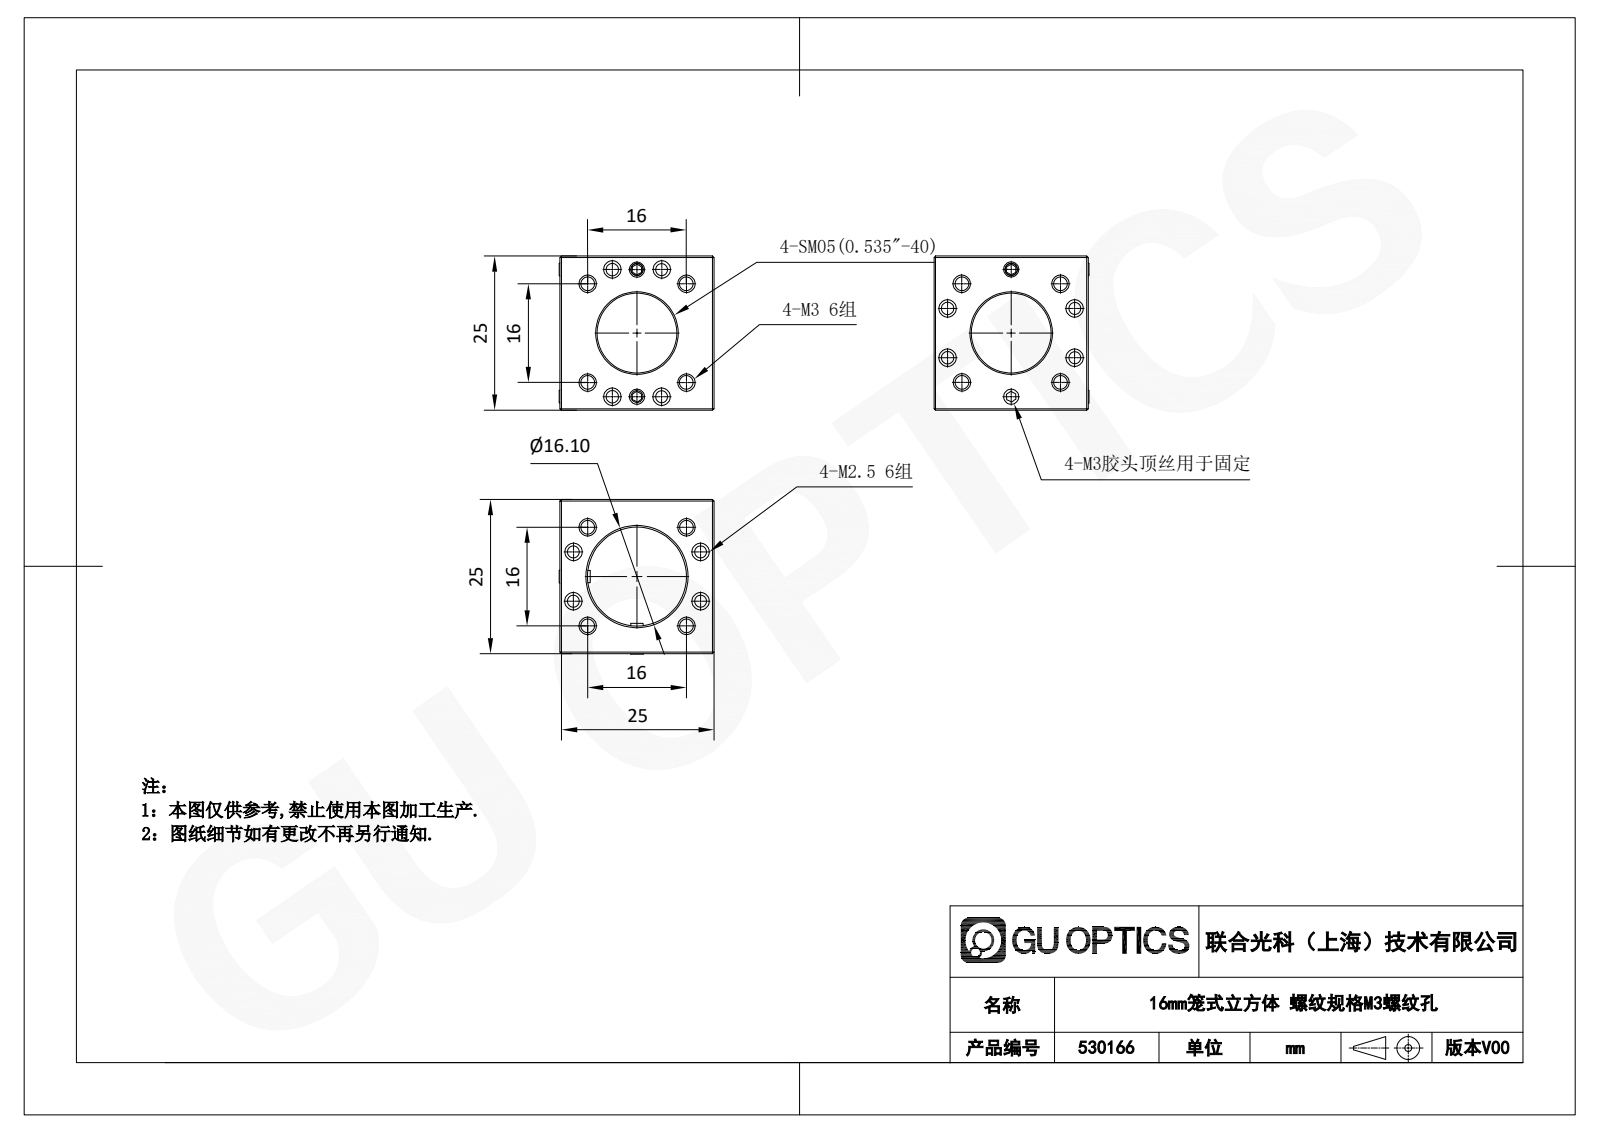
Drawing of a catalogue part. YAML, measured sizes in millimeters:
part_name: "530166"
step_written_by: "SolidWorks 2020 (CONFIG_CONTROL_DESIGN)"
units: millimeters
bodies: {solids: 5, faces: 378, planar: 62, cylindrical: 210, other: 106}
overall_size: [25.09, 25.09, 25]
volume: 6879
surface_area: 6150
round_holes:
  - {diameter: 2.5, count: 16}
  - {diameter: 2.05, count: 12}
  - {diameter: 12.95, count: 2}
  - {diameter: 16.1, count: 1}
round_bosses_or_shafts:
  - {diameter: 3, count: 4}
  - {diameter: 2, count: 4}
face_to_face_distances: [25, 35, 4.91, 20.09, 1.5, 0.91, 4, 24.09, 1, 5]
hole_center_spacings: [4.61, 11.05, 11.31, 12.22, 16, 18.73, 21.88, 8.32]
